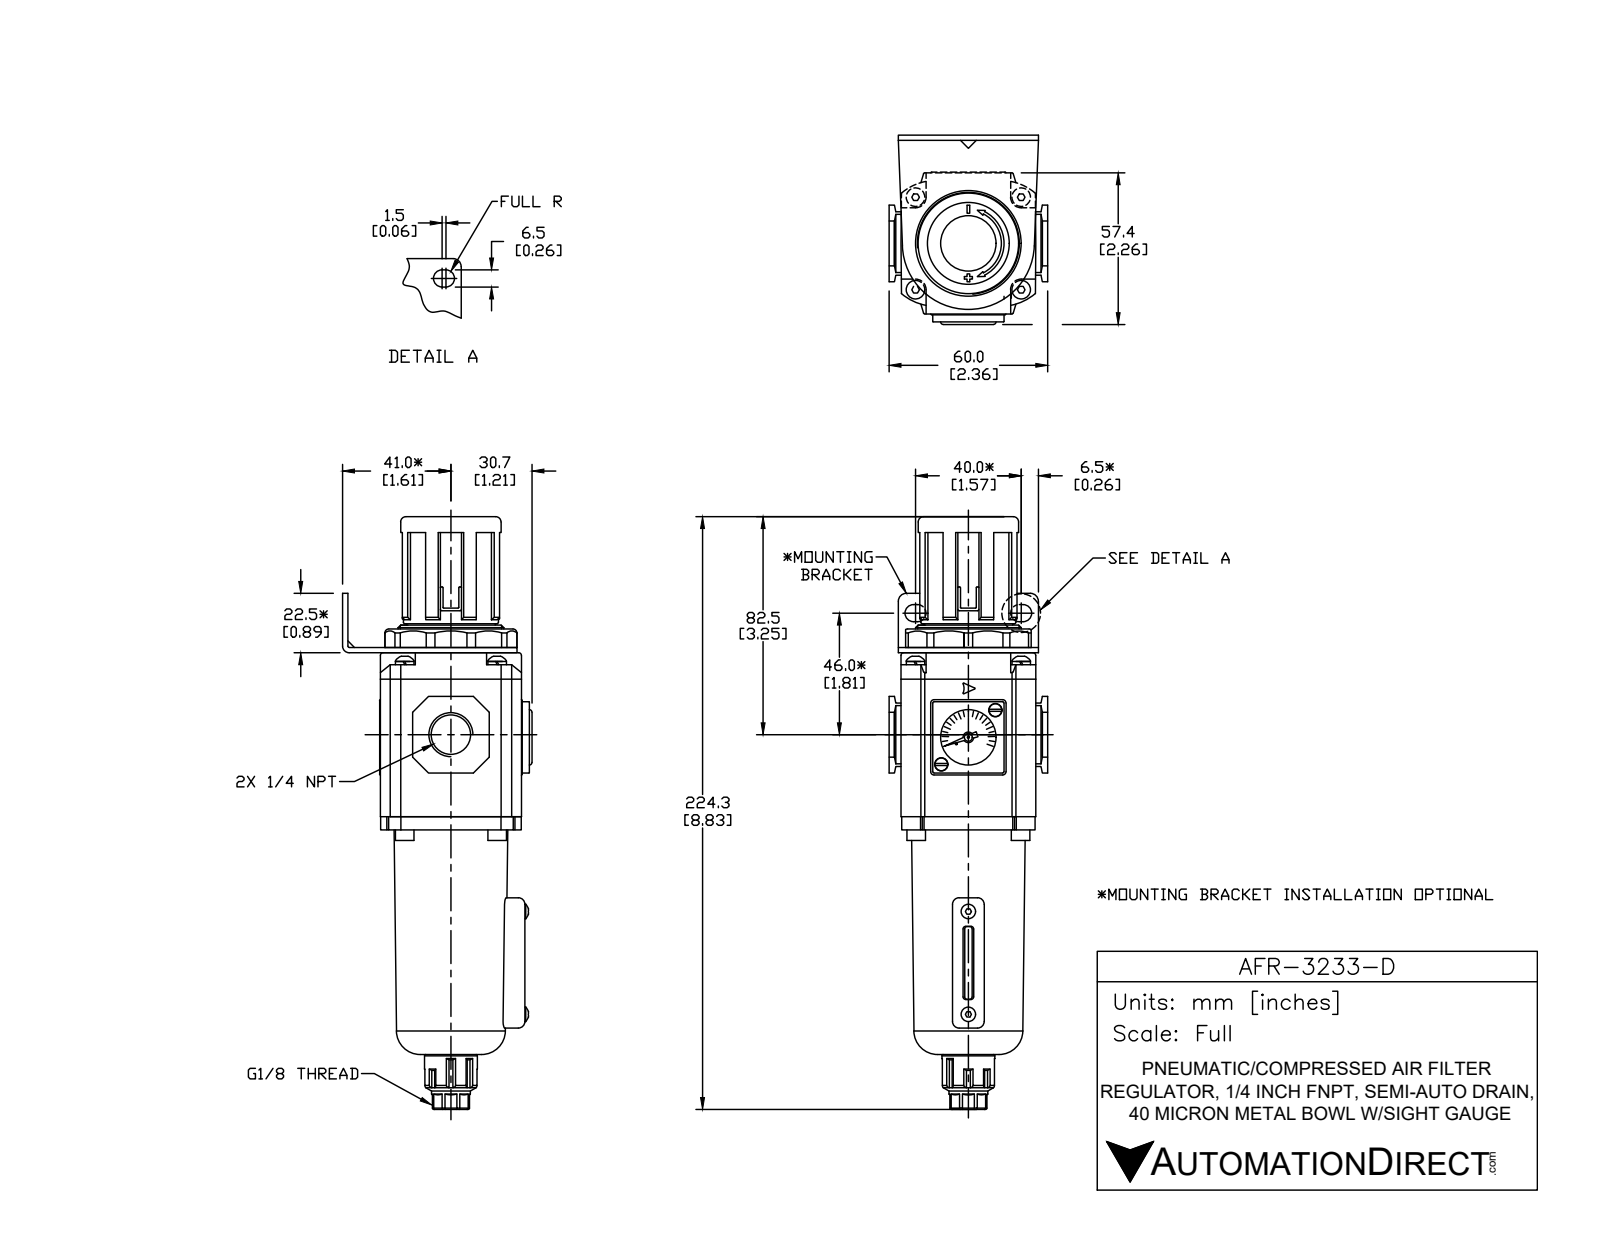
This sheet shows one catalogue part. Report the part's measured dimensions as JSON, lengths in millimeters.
{"part_name": "AFR-3233-D", "step_written_by": "SolidWorks 2015 (CONFIG_CONTROL_DESIGN)", "units": "millimeters", "bodies": {"solids": 16, "faces": 687, "planar": 418, "cylindrical": 181, "other": 88}, "overall_size": [224.3, 72, 60], "volume_mm3": 361874, "surface_area_mm2": 64386, "round_holes": [[3, 6], [2, 1], [6.2, 1], [11.13, 1], [21, 1], [30, 1], [32, 1]], "round_bosses_or_shafts": [[5.5, 6], [7, 4], [2.7, 2], [40, 1], [38, 1], [36, 1], [33.5, 1], [20.46, 1]], "partial_cylinders_radius": [[1, 16], [1.2, 10], [1.3, 8], [2.5, 8], [9.5, 8], [19.9, 8], [0.5, 6], [3.25, 6]], "face_to_face_distances": [2, 62, 64, 53.4, 51, 1, 55.5, 52.4, 4.5, 67], "hole_center_spacings": [26.58, 14.5, 35, 40, 53.15, 28.99]}
